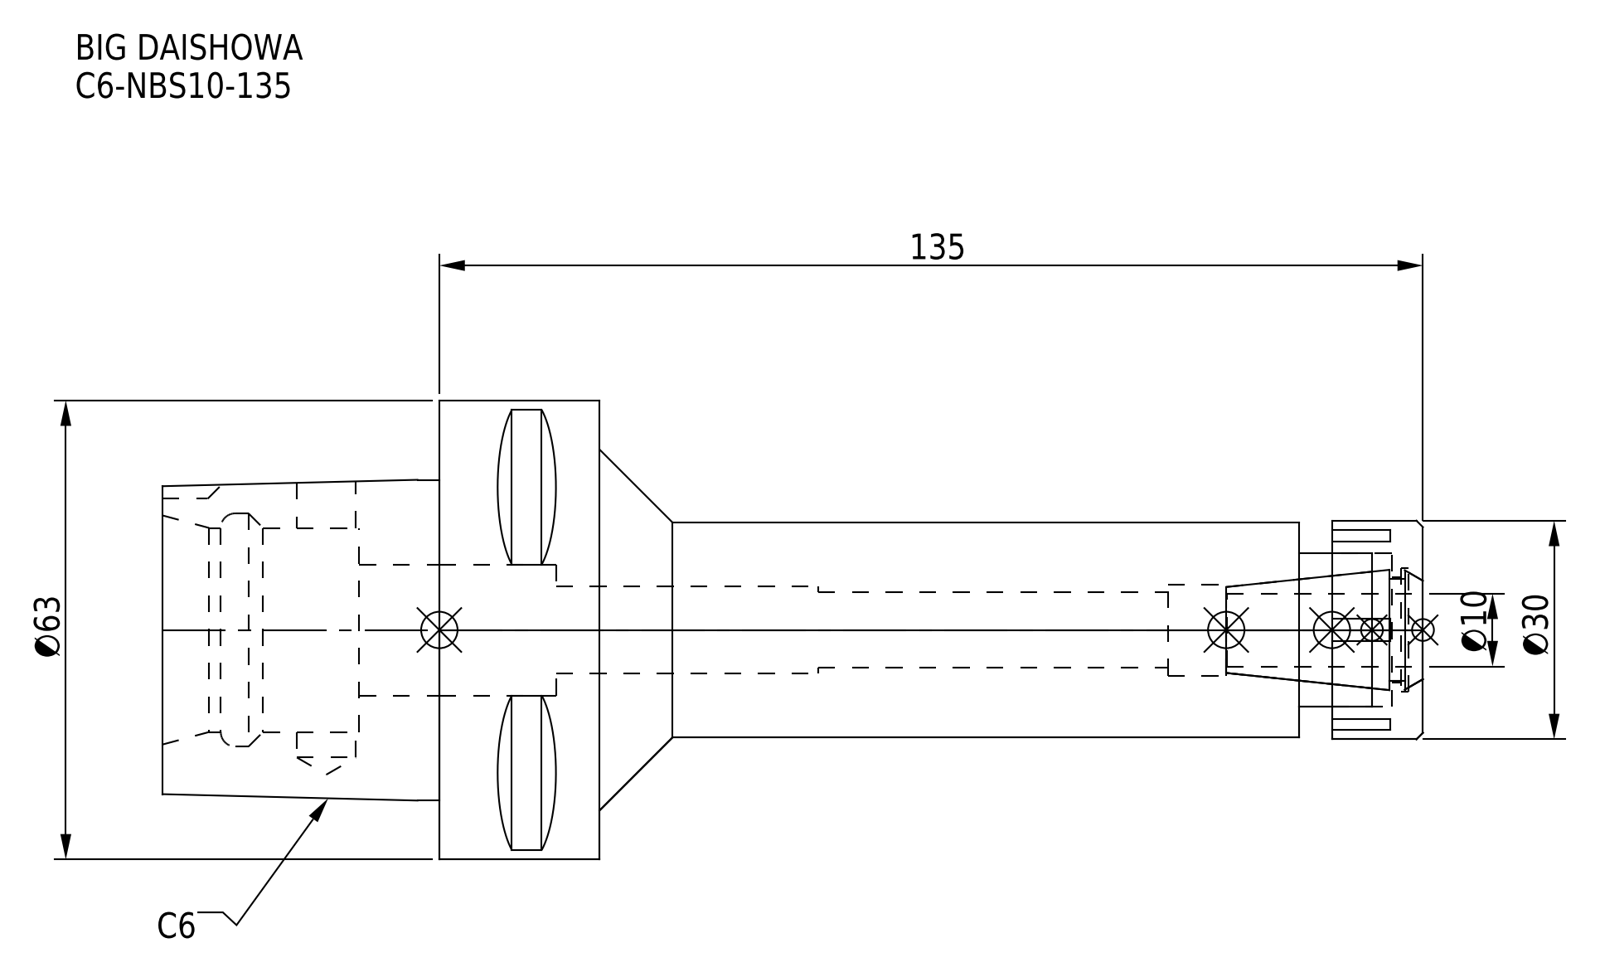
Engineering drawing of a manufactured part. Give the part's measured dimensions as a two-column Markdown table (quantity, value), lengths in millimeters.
| quantity | value |
| --- | --- |
| part name | NBN10_1.stp; C6-NBS10-135.stp; C6-NBS10-135_1.stp; C6-NBS10-135-FreeParts (+3 more) |
| STEP written by | SolidWorks 2019 (CONFIG_CONTROL_DESIGN) |
| units | millimeters |
| bodies | 2 solids, 112 faces (61 planar, 33 cylindrical, 18 other) |
| overall size | 173 × 63 × 63 |
| volume | 164 051 mm³ |
| surface area | 36 438 mm² |
| round holes (diameter × count) | 8.1 × 1, 10.4 × 1, 12 × 1, 12.5 × 1, 14.5 × 1, 17 × 1, 18 × 1, 21 × 1, 28 × 1, 32 × 1 |
| round bosses / shafts (diameter × count) | 63 × 1, 30 × 1, 29.5 × 1 |
| partial cylindrical surfaces (radius × count) | 5 × 1 |
| main face-to-face distances | 22, 27, 60, 38, 113, 135, 173, 33, 146, 11 |
